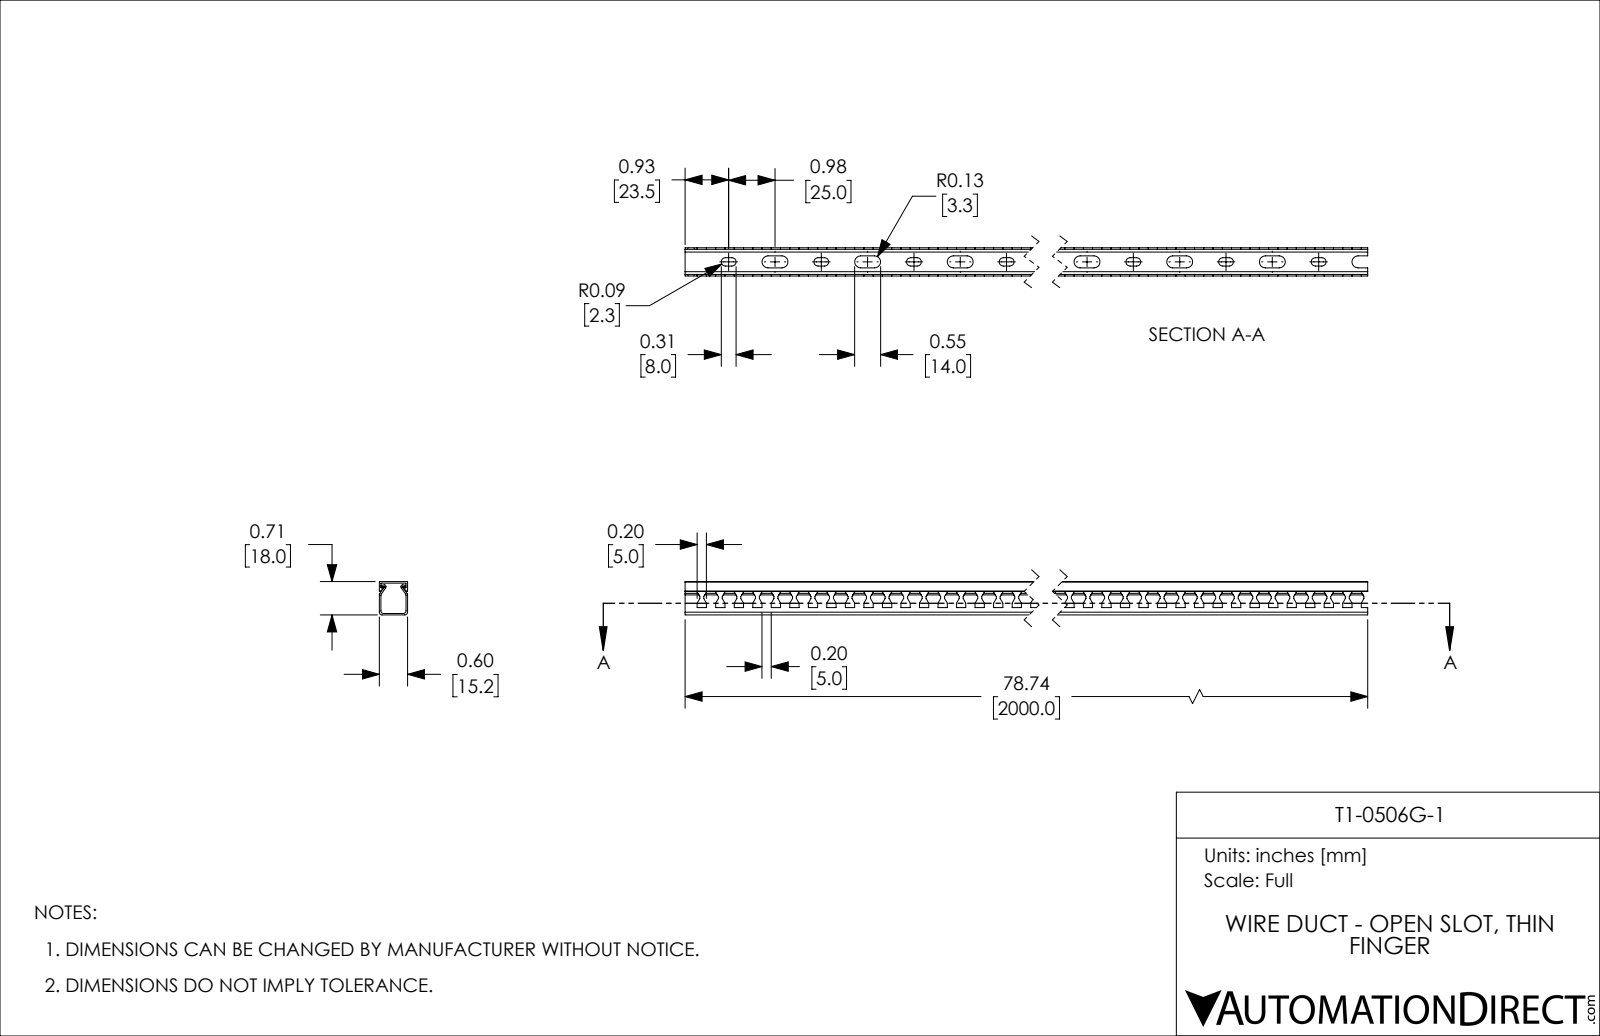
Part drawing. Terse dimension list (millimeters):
name: T1-0506G-1
written by: SolidWorks 2021 (CONFIG_CONTROL_DESIGN)
unit: mm
bodies: 2 solids, 963 faces (513 planar, 450 cylindrical, 0 other)
size: 2000 × 18 × 15.2
volume: 120 444 mm³; area: 297 721 mm²
rounds: 80× R2.25, 79× R3.25, 20× R1, 12× R1.5, 10× R0.25, 8× R0.38
face distances: 0.8, 14.4, 17.2, 15.2, 13.6, 18, 16.4, 7.57, 8.37, 4.35
